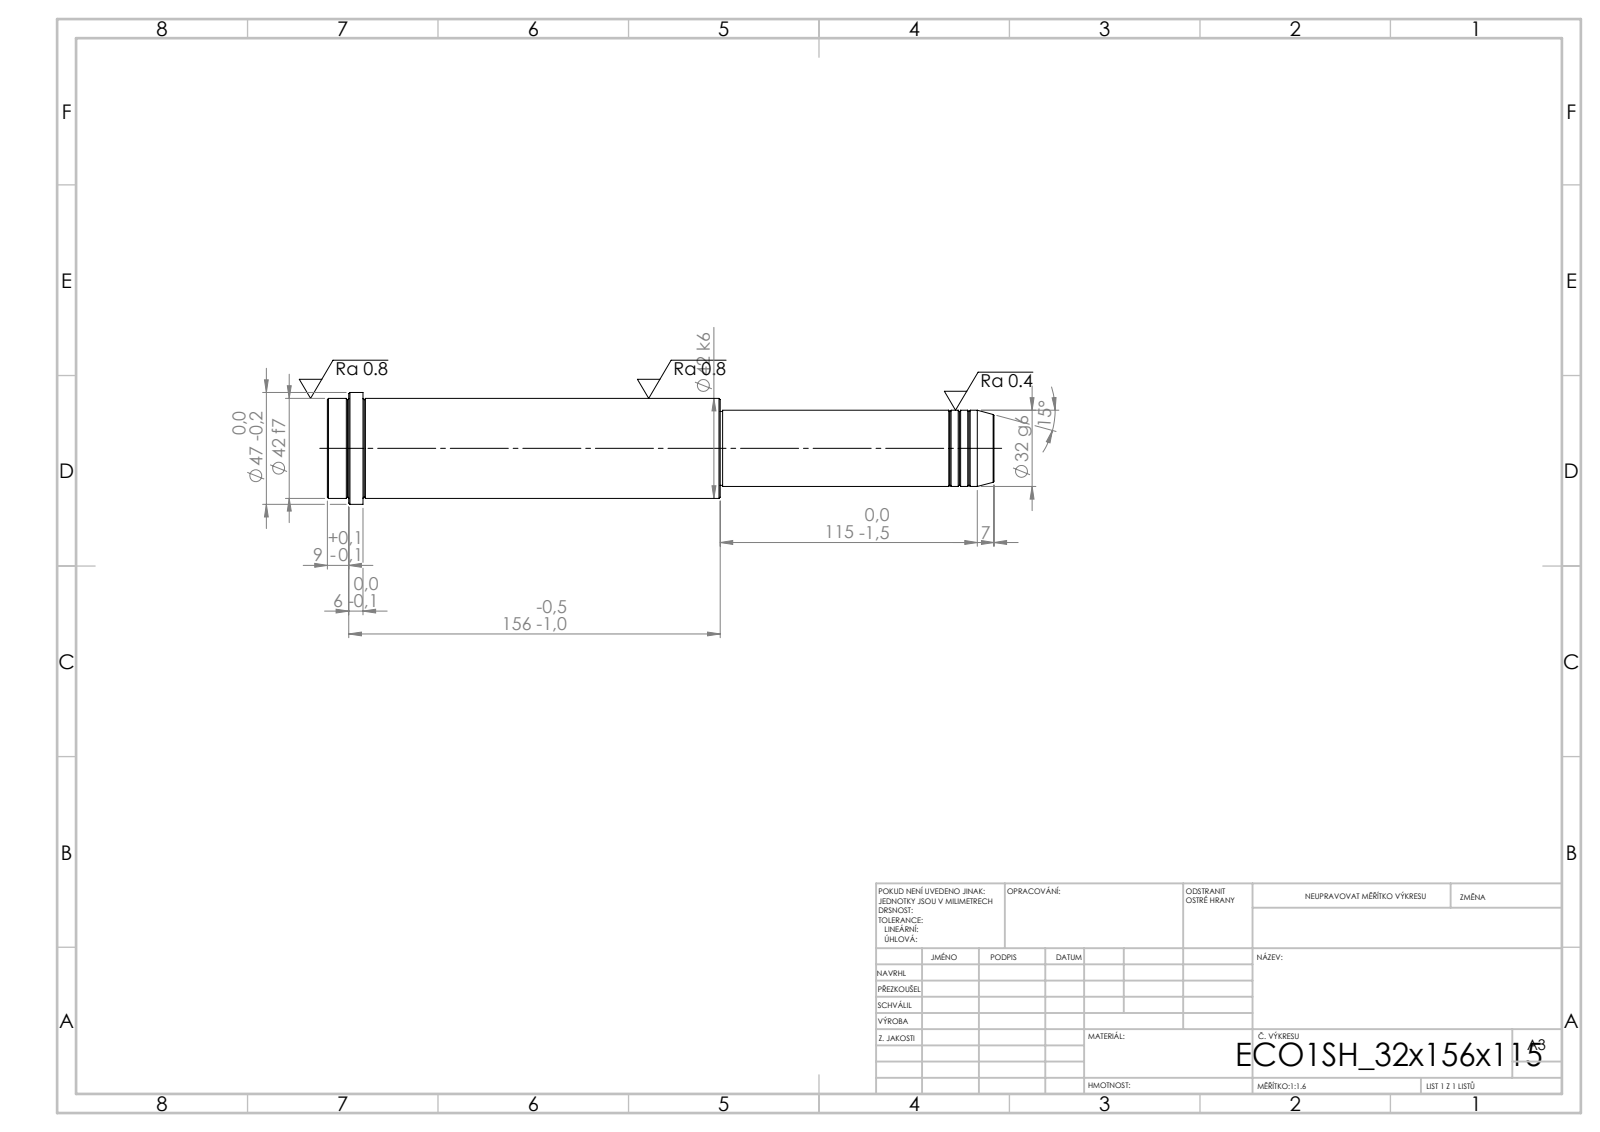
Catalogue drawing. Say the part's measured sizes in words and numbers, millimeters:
Its 3-D file was written by "SolidWorks 2019 (CONFIG_CONTROL_DESIGN)". It is 1 solid with 52 faces: 6 planar, 16 cylindrical and 30 other. Overall it measures 280 by 47 by 47 millimeters. Its volume is 322 227 cubic millimeters and its surface area 36 972 square millimeters. Round bosses or shafts: 1 of diameter 47, 1 of diameter 42, 1 of diameter 32, 1 of diameter 31. The main face-to-face distances are 280, 115, 165, 265, 150, 15, 271, 156, 6, 9.
